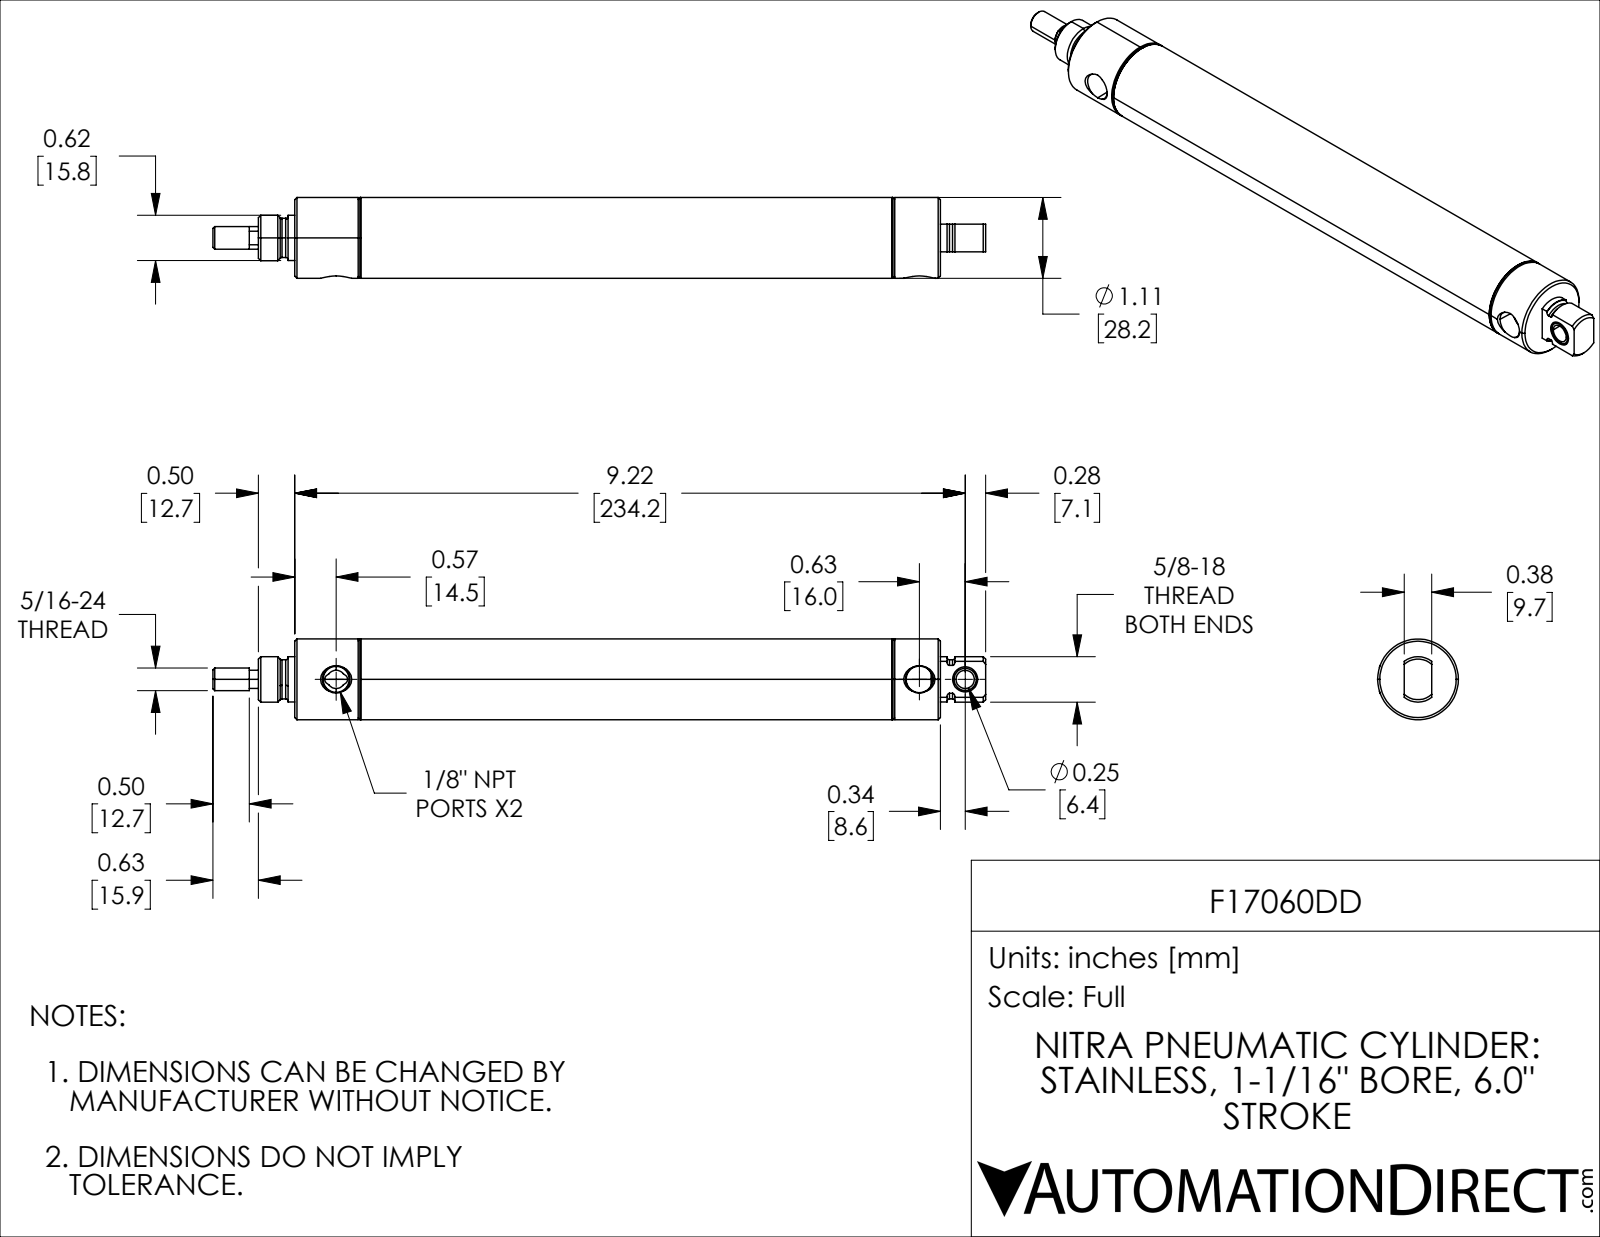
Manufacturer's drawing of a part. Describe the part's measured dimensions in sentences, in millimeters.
The part is named "F17060DD_5; F17060DD; F17060DD_3; F17060DD_7 (+2 more)". Its 3-D file was written by "SolidWorks 2021 (CONFIG_CONTROL_DESIGN)". It is 5 solids with 156 faces: 30 planar, 58 cylindrical and 68 other. Overall it measures 269.88 by 28.19 by 28.19 millimeters. Its volume is 59 773 cubic millimeters and its surface area 52 470 square millimeters. Round holes: 1 of diameter 6.38, 1 of diameter 8.53, 1 of diameter 8.78, 1 of diameter 9.25, 1 of diameter 9.53, 1 of diameter 19.05, 1 of diameter 25.7. Round bosses or shafts: 1 of diameter 28.19, 1 of diameter 27.23, 1 of diameter 15.88, 1 of diameter 15.81, 1 of diameter 13.68, 1 of diameter 7.94, 1 of diameter 7.92. Partial cylindrical surfaces (rounded edges, fillets, slot ends): 1 of radius 3.17, 1 of radius 6.84. The main face-to-face distances are 22.22, 152.4, 174.62, 196.95, 44.55, 22.33, 28.58, 180.98, 203.2, 225.53. The hole center spacings are 16.01.
